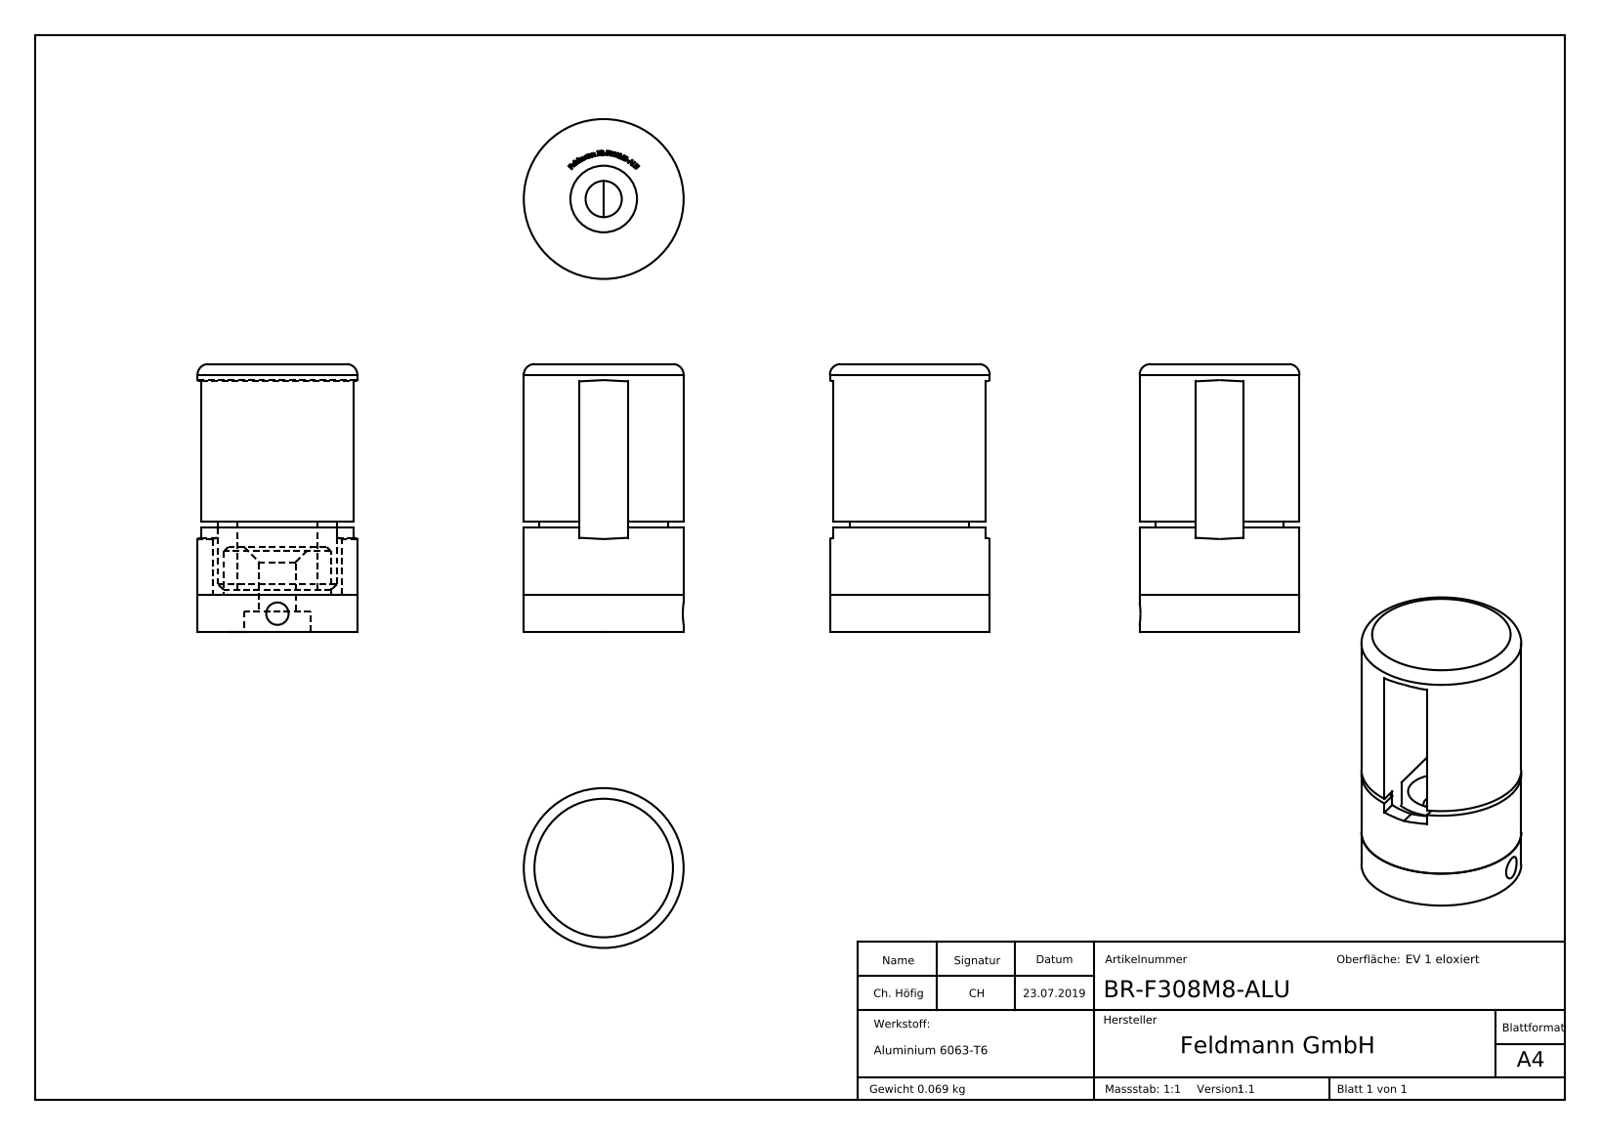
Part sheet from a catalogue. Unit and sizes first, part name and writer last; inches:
Units: inches
Overall size (bounding box): 2.533 × 1.181 × 1.181
Round holes (diameter × count): ⌀0.165 ×1, ⌀0.268 ×1, ⌀0.492 ×1, ⌀0.953 ×1
Round bosses / shafts (diameter × count): ⌀1.181 ×1, ⌀0.787 ×1
Partial cylindrical surfaces — rounded edges, fillets, slot ends (radius × count): R0.344 ×1, R0.474 ×1
Main face-to-face distances: 0.354, 0.276, 1.982, 1.706, 0.039, 0.5, 0.815, 0.539, 1.167, 0.315
Volume: 1.553 in³ · Surface area: 18.72 in²
Bodies: 3 solids, 329 faces (195 planar, 12 cylindrical, 122 other)
Part name (STEP PRODUCT): BR-R1XM8-XXX Teil2_BR-F308M8-ALU Teil2; BR-R1XM8-XXX Teil1_BR-FXXXM8-ALU Teil1; BR-R1XM8-XXX Teil3_BR-F308M8-ALU Teil3; BR-F308M8-ALU (+3 more)
STEP written by: SolidWorks 2015 (CONFIG_CONTROL_DESIGN)
